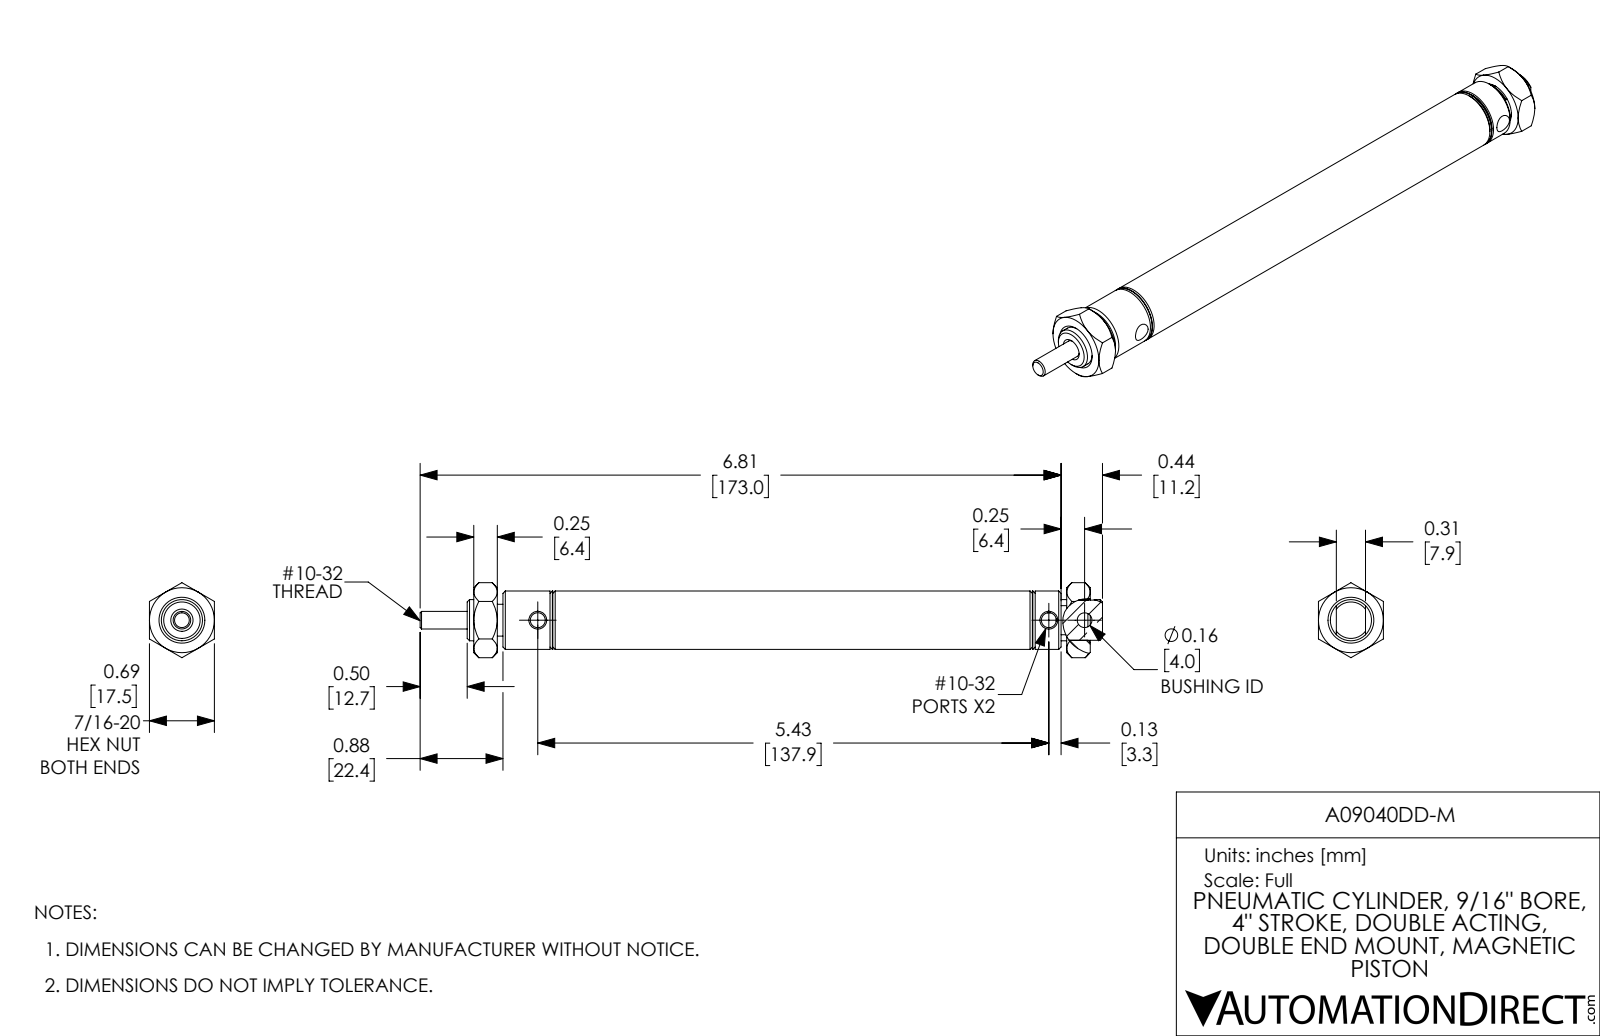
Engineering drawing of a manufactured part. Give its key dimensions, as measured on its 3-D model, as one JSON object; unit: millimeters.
{"part_name": "A09040DD-M_Mounting Nut_D-154; A09040DD-M-Rod; A09040DD-M-MainBody; A09040DD-M", "step_written_by": "SolidWorks 2017 (AUTOMOTIVE_DESIGN)", "units": "millimeters", "bodies": {"solids": 4, "faces": 151, "planar": 36, "cylindrical": 46, "other": 69}, "overall_size": [184.2, 20.2, 17.5], "volume_mm3": 18340, "surface_area_mm2": 19700, "round_holes": [[4, 2], [4.8, 2], [4, 1], [4, 1], [4.7, 1], [14.3, 1]], "round_bosses_or_shafts": [[15.7, 1], [11.1, 1], [8.6, 1]], "face_to_face_distances": [17.5, 12.7, 6.4, 160, 18.2, 132.5, 134, 7.9, 114.3, 19.7], "hole_center_spacings": [9.7, 137.9, 147.6]}
